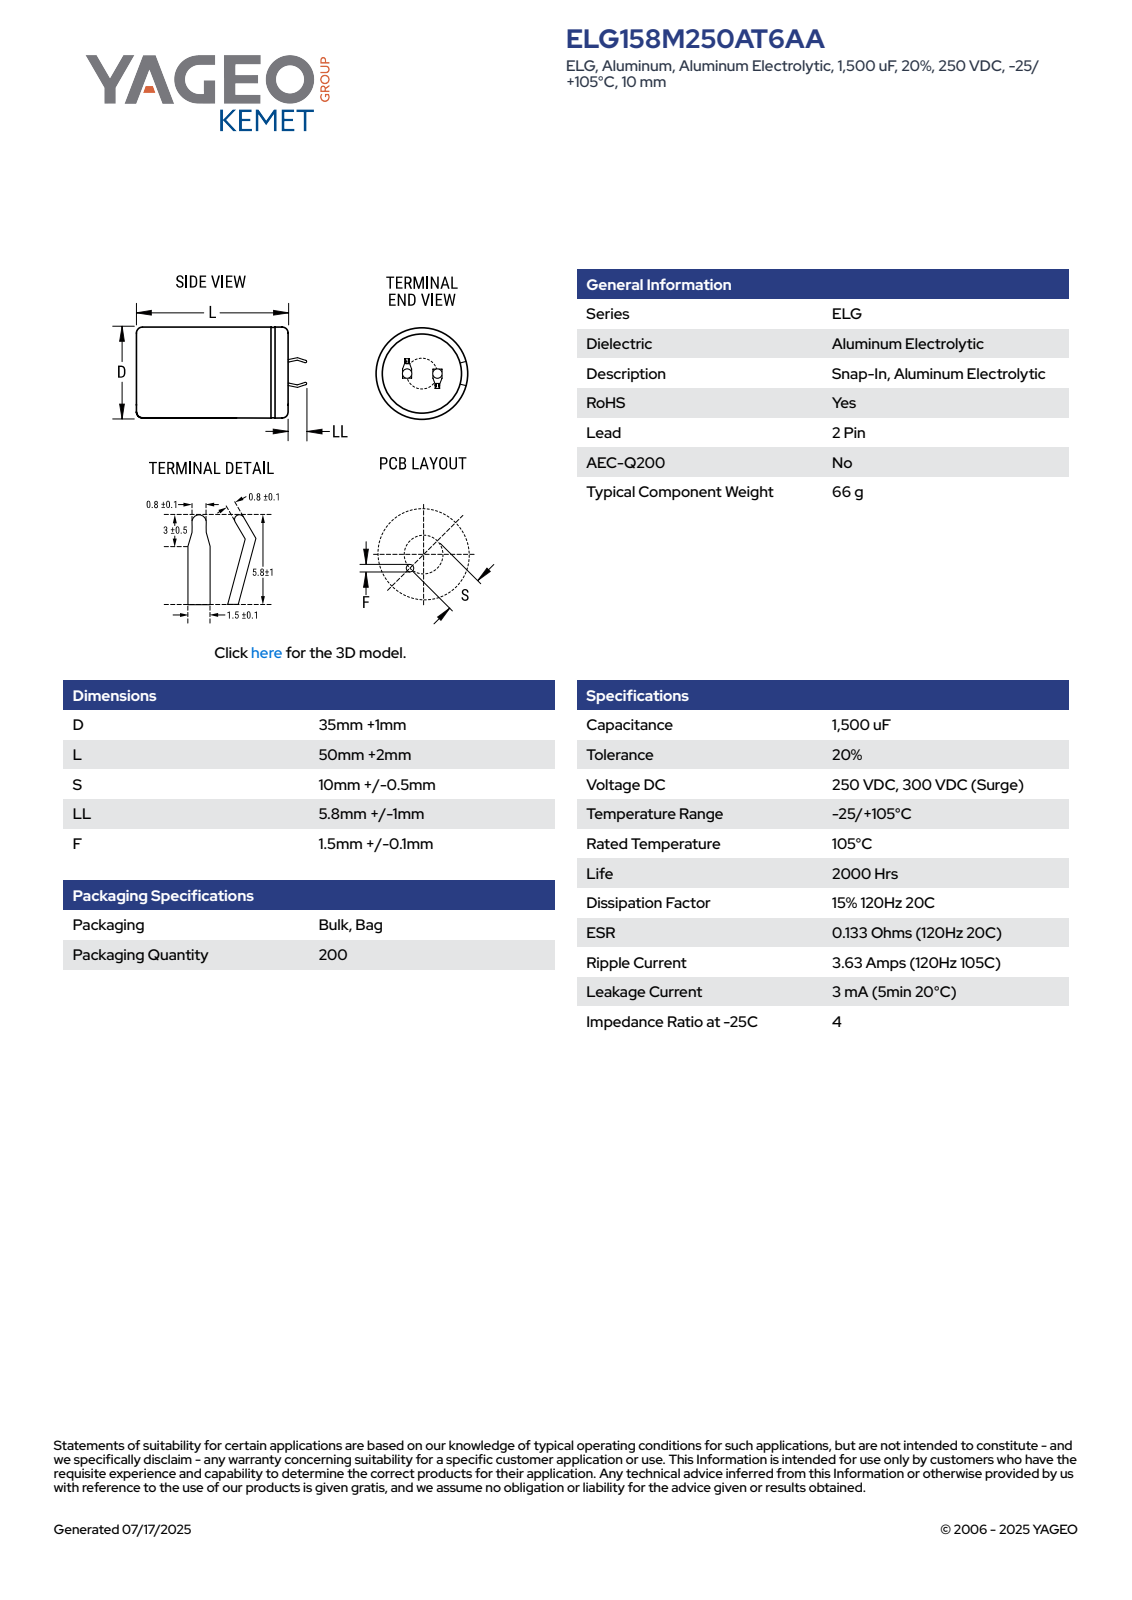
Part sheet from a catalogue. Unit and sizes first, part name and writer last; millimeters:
Units: millimetres
Overall size (bounding box): 58.79 × 36 × 36
Round holes (diameter × count): ⌀31.85 ×1
Round bosses / shafts (diameter × count): ⌀36 ×1
Partial cylindrical surfaces — rounded edges, fillets, slot ends (radius × count): R17.99 ×1
Main face-to-face distances: 51.99, 0.6, 52.49, 0.5, 7.08, 7.63, 0.75, 1.35, 7.68, 6.48
Volume: 52 401 mm³ · Surface area: 7 912 mm²
Bodies: 1 solid, 100 faces (52 planar, 9 cylindrical, 39 other)
Part name (STEP PRODUCT): CARS_K2P_35X50_D36L52S10LL6.8F1.6
STEP written by: SolidWorks 2014 (AUTOMOTIVE_DESIGN)
